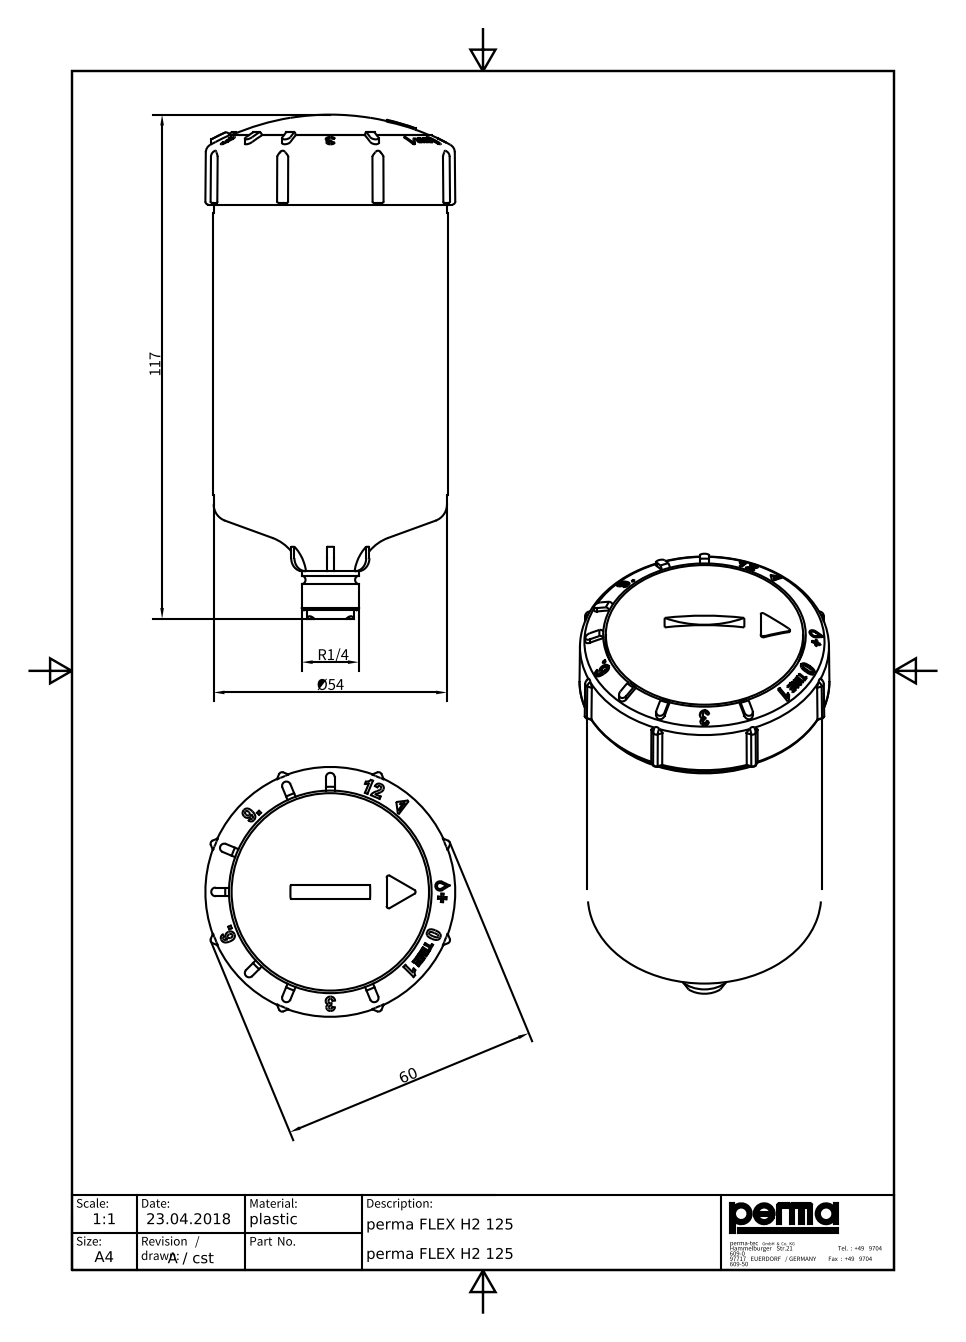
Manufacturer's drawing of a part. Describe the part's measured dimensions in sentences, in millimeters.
The part is named "FLEX H2 125". Its 3-D file was written by "Autodesk Inventor 2018 (CONFIG_CONTROL_DESIGN)". It is 1 solid with 358 faces: 153 planar, 44 cylindrical and 161 other. Overall it measures 116.48 by 57.72 by 57.72 millimeters. Its volume is 218 582 cubic millimeters and its surface area 21 450 square millimeters. Round holes: 1 of diameter 46.8. Round bosses or shafts: 1 of diameter 53.9, 1 of diameter 45.6, 1 of diameter 13.16, 1 of diameter 11. Partial cylindrical surfaces (rounded edges, fillets, slot ends): 16 of radius 0.3, 7 of radius 1, 6 of radius 3, 3 of radius 0.2, 3 of radius 0.5, 1 of radius 0.7, 1 of radius 1.08, 1 of radius 20. The main face-to-face distances are 95.7, 1.5, 2, 3.1, 9, 11, 93.7, 84.7, 20, 1.75.
